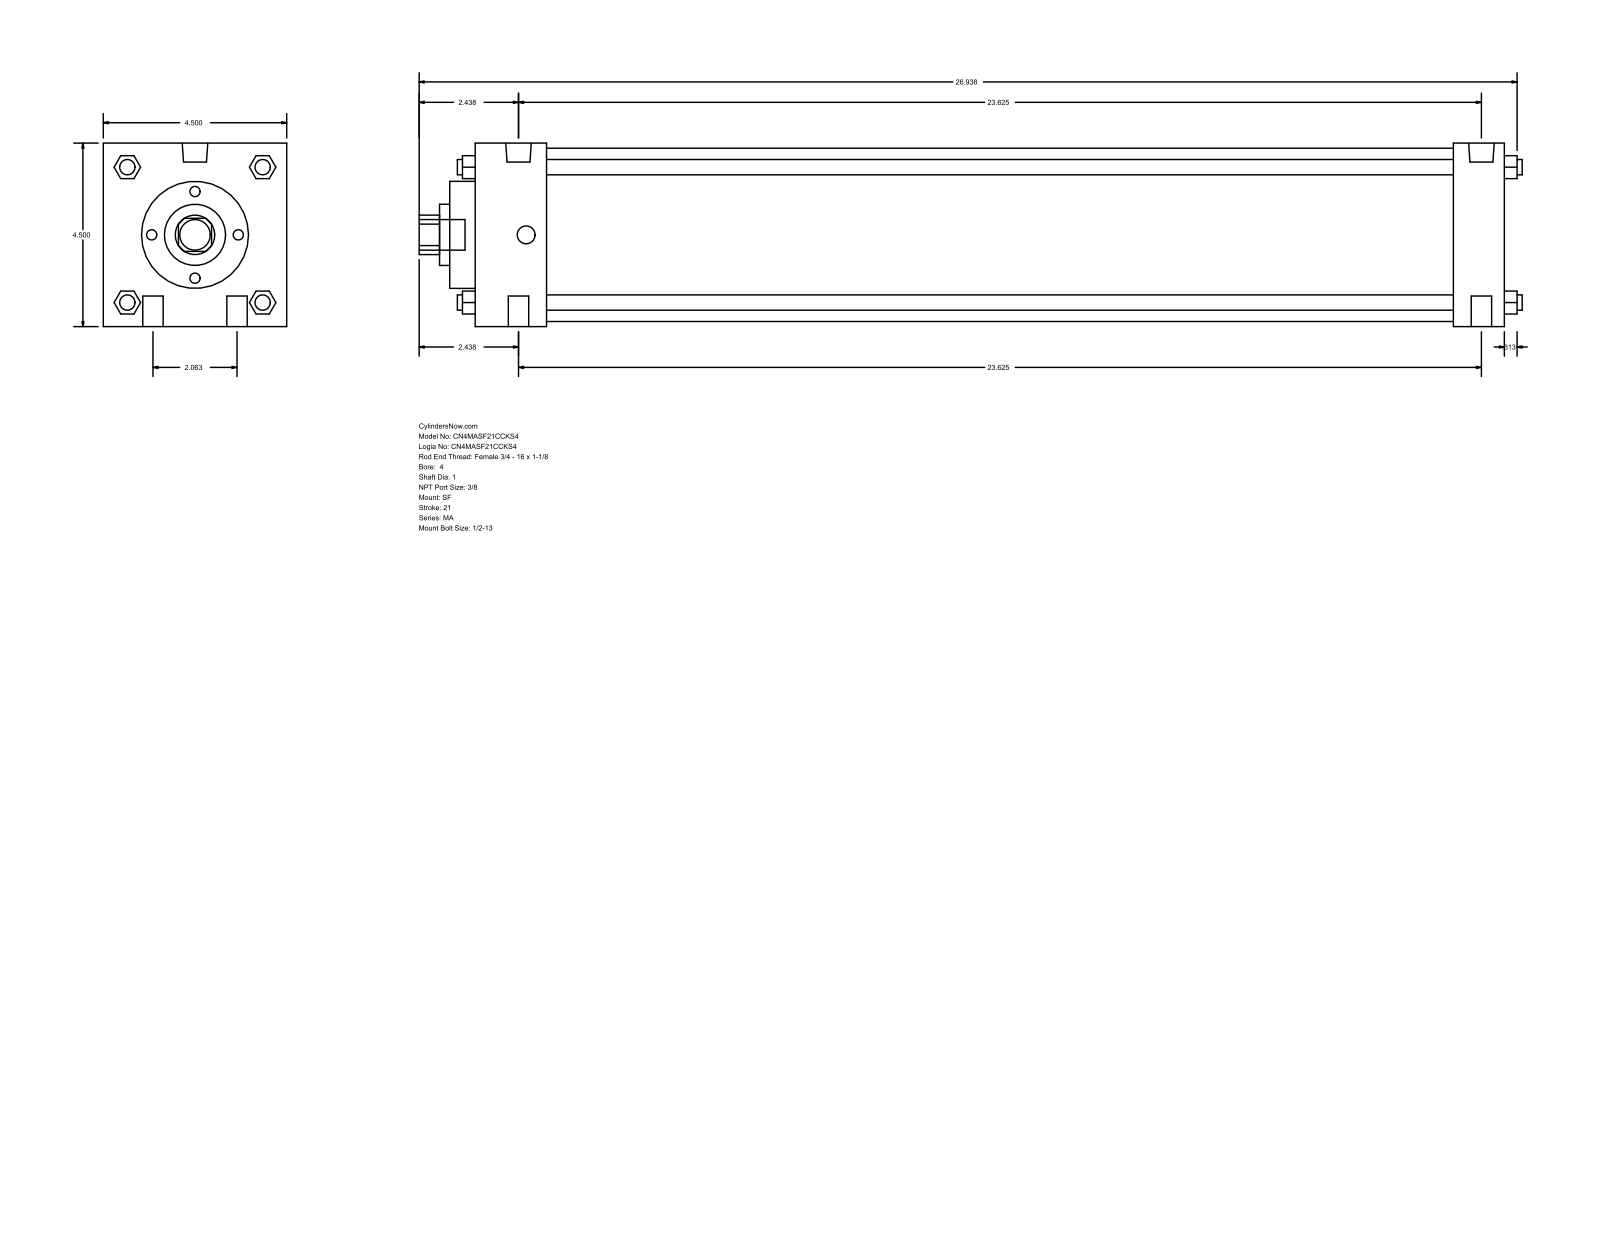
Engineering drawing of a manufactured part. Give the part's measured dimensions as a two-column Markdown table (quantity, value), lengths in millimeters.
| quantity | value |
| --- | --- |
| part name | MA_SF__0400_1 |
| STEP written by | GSSL Pune (CONFIG_CONTROL_DESIGN) |
| units | millimeters |
| bodies | 0 solids, 126 faces (95 planar, 31 cylindrical, 0 other) |
| overall size | 687.39 × 114.3 × 114.3 |
| round holes (diameter × count) | 25.4 × 1, 38.1 × 1, 66.67 × 1, 107.95 × 1 |
| round bosses / shafts (diameter × count) | 12.7 × 4, 9.53 × 4, 15.93 × 2, 11.11 × 2, 19.05 × 1 |
| partial cylindrical surfaces (radius × count) | 12.29 × 1 |
| main face-to-face distances | 114.3, 641.35, 609.6, 31.75, 44.46, 565.14, 596.89, 657.22, 15.87, 60.33 |
